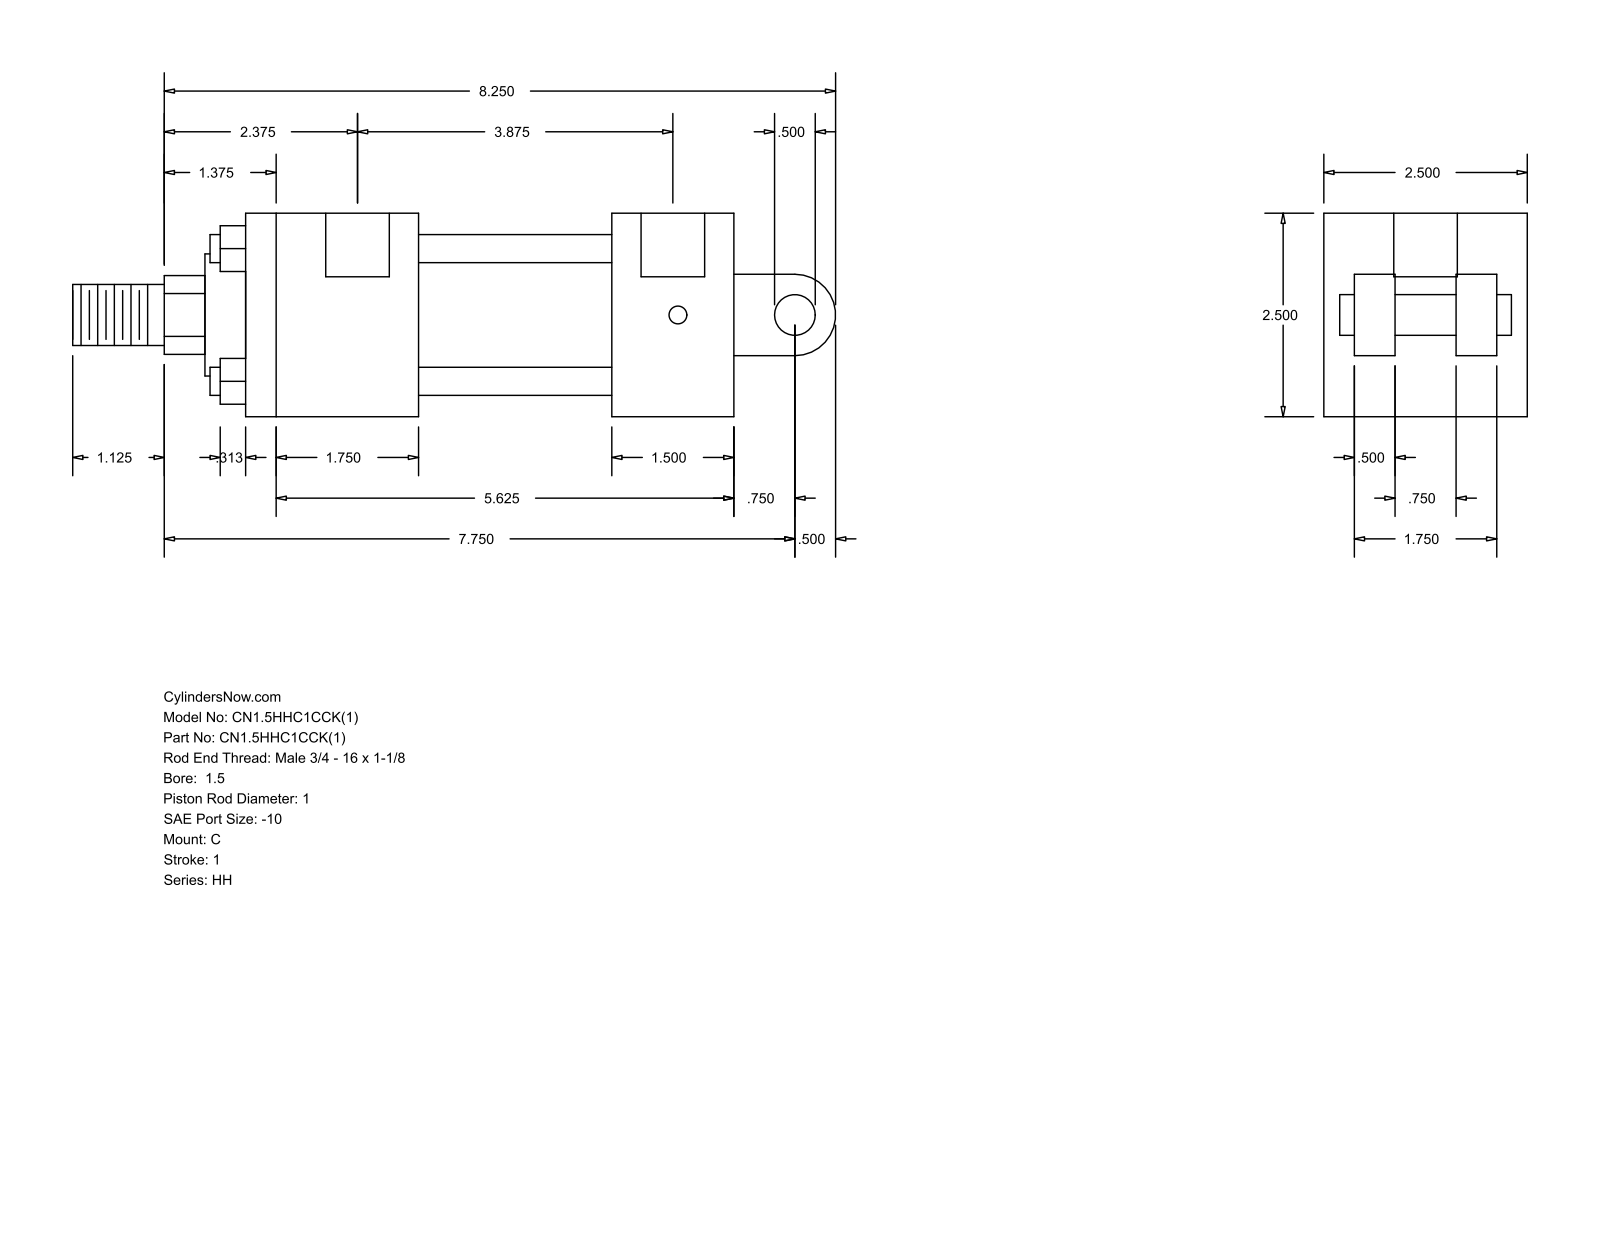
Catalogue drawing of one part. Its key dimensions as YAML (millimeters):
part_name: "HH_C__0150_1"
step_written_by: "GSSL Pune (CONFIG_CONTROL_DESIGN)"
units: millimeters
bodies: {solids: 0, faces: 99, planar: 70, cylindrical: 29, other: 0}
overall_size: [238.12, 63.5, 63.5]
round_holes:
  - {diameter: 5.56, count: 4}
  - {diameter: 19.84, count: 2}
round_bosses_or_shafts:
  - {diameter: 8.76, count: 4}
  - {diameter: 44.45, count: 1}
  - {diameter: 38.1, count: 1}
  - {diameter: 25.4, count: 1}
  - {diameter: 19.05, count: 1}
  - {diameter: 12.7, count: 1}
partial_cylinders:
  - {radius: 12.29, count: 1}
  - {radius: 12.7, count: 1}
face_to_face_distances: [63.5, 53.98, 38.1, 60.32, 98.42, 114.3, 152.4, 12.7, 9.52, 22.22]
hole_center_spacings: [1.59, 100.01, 101.6, 98.42]
